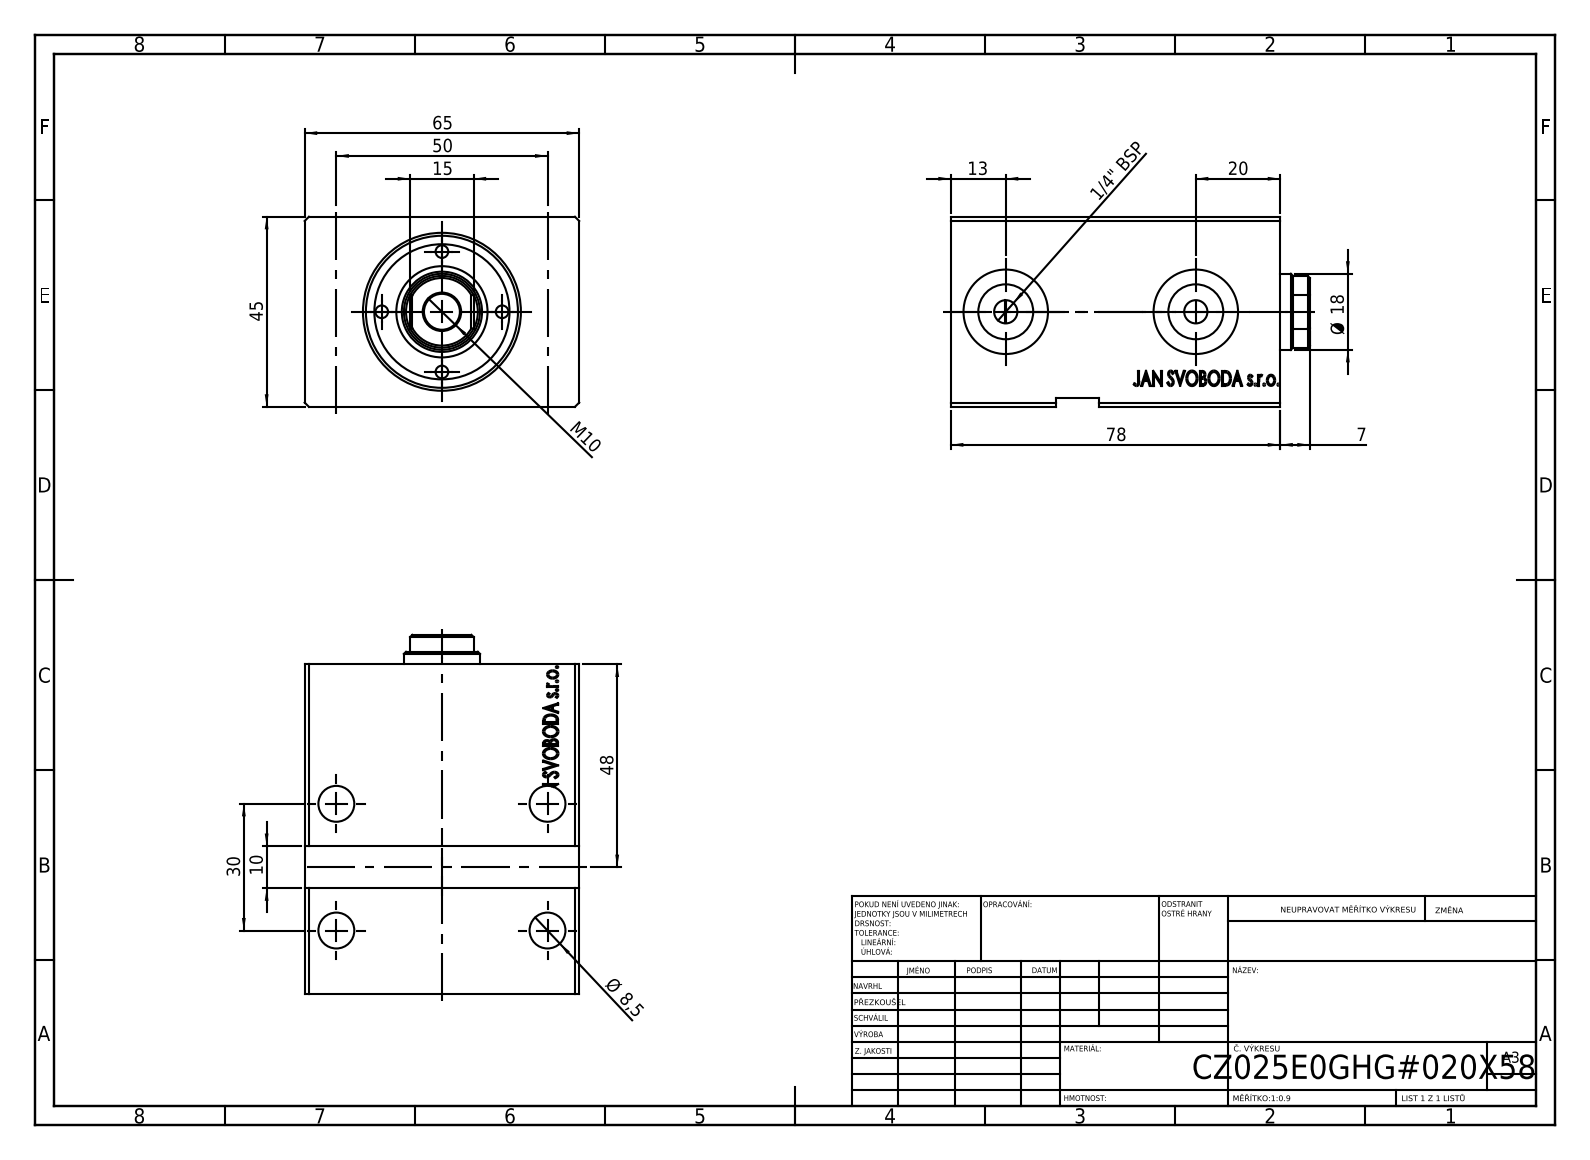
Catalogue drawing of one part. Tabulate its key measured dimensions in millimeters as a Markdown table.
| quantity | value |
| --- | --- |
| STEP written by | SolidWorks 2019 (CONFIG_CONTROL_DESIGN) |
| units | millimeters |
| bodies | 1 solid, 754 faces (350 planar, 32 cylindrical, 372 other) |
| overall size | 78 × 65 × 45 |
| volume | 177 182 mm³ |
| surface area | 33 758 mm² |
| round holes (diameter × count) | 8.5 × 4, 5.5 × 2, 8 × 2, 13 × 2, 20 × 2, 25 × 1, 36 × 1 |
| main face-to-face distances | 45, 65, 78, 77.8, 43, 2, 7, 70.8, 71, 65.2 |
| hole center spacings | 30, 50, 58.31, 16.28, 17.89, 25, 27.2, 34.13 |
